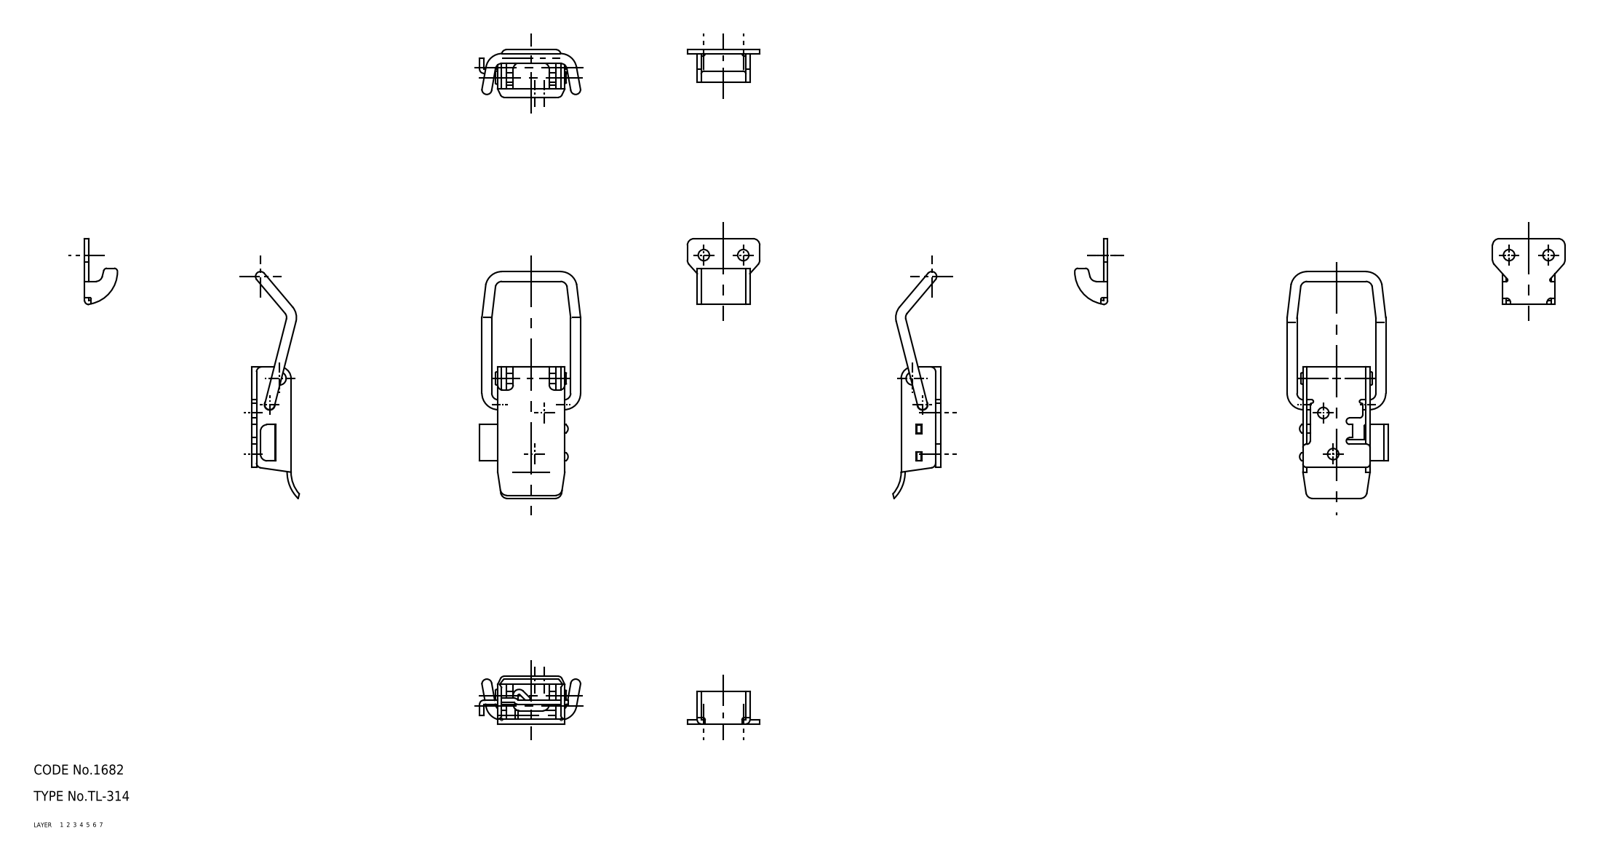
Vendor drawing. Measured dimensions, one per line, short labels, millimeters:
name: TL_314
written by: SolidWorks 2003240 (AUTOMOTIVE_DESIGN)
unit: mm
bodies: 8 solids, 266 faces (126 planar, 112 cylindrical, 28 other)
size: 79 × 30.7 × 15.26
volume: 4 693 mm³; area: 8 453 mm²
holes: 4× ⌀3.4, 1× ⌀3, 1× ⌀3.1, 1× ⌀3.2
bosses: 6× ⌀3
rounds: 16× R1, 9× R1.5, 9× R2, 8× R0.5, 8× R1.2, 2× R0.3, 2× R0.8, 2× R10
face distances: 1.2, 10.8, 1.5, 6, 4.8, 10.5, 19.2, 12, 9.3, 18
hole spacings: 8.54, 12, 12.85, 48.04, 49.03, 60.71, 60.9
